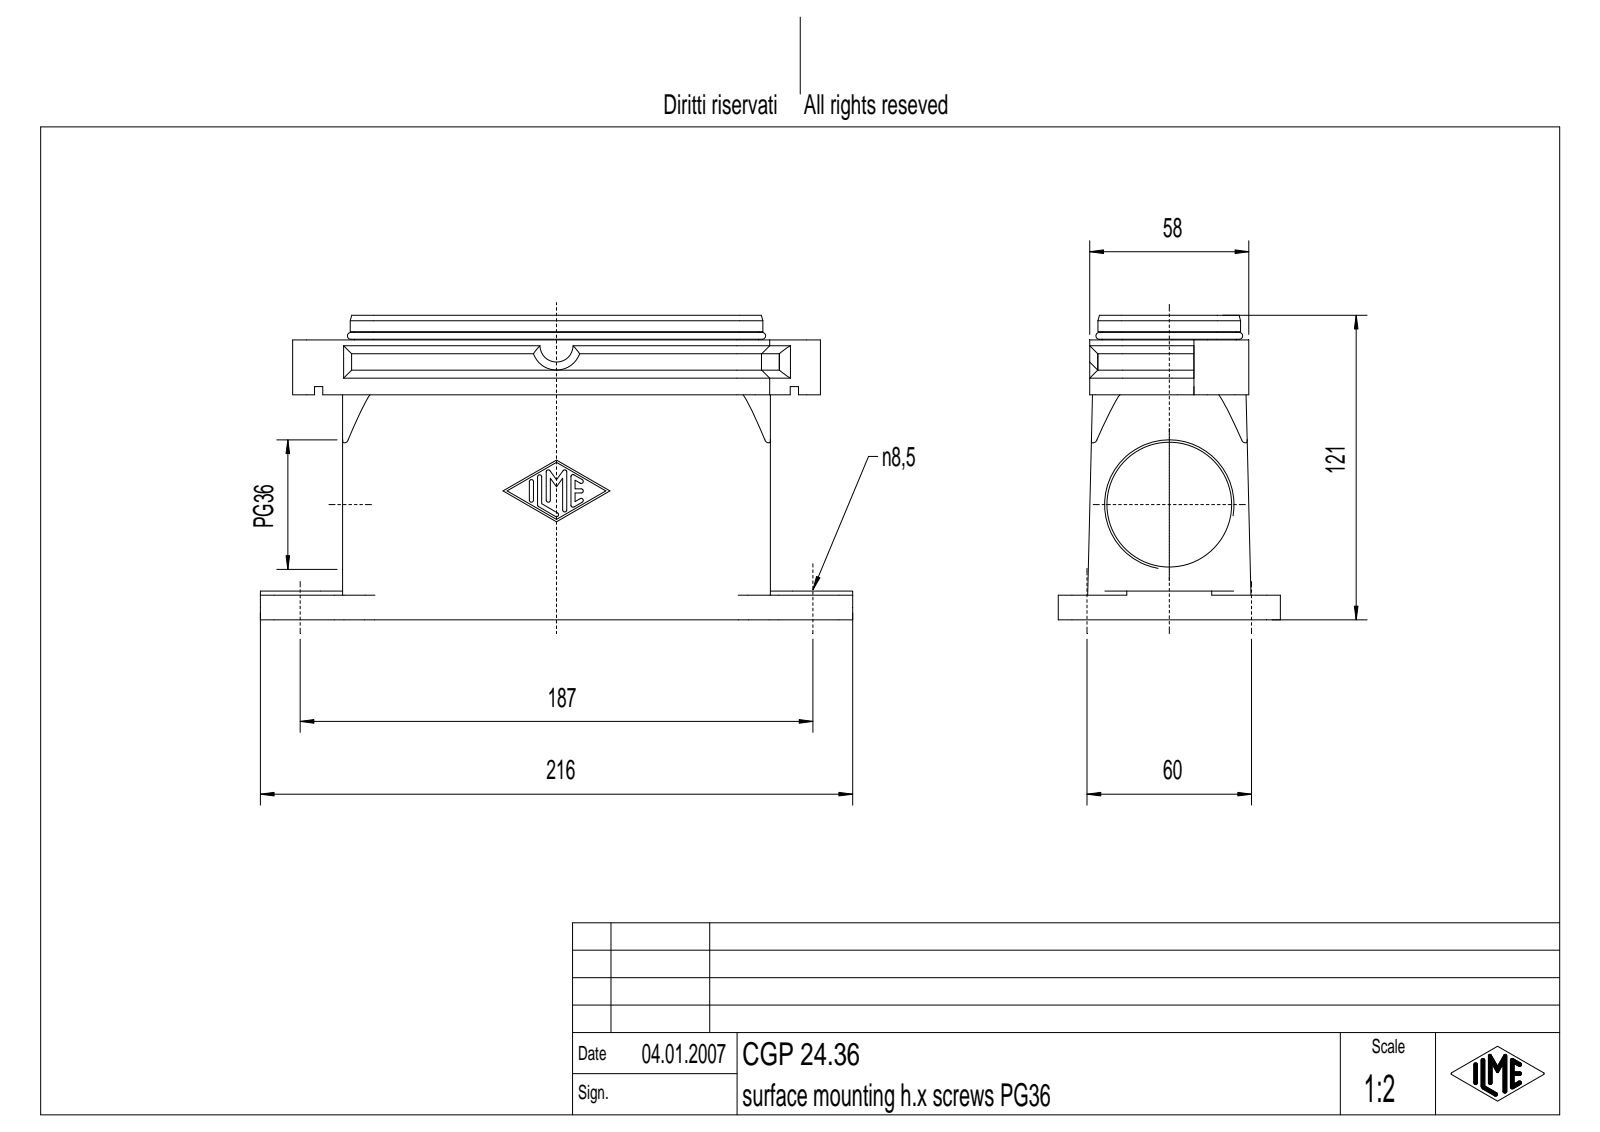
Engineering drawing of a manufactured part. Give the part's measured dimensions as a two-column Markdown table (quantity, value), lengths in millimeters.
| quantity | value |
| --- | --- |
| part name | MSBO9681 |
| STEP written by | CoCreate Modeling 16.00A 16-Aug-2008 (C) Parametric Technology GmbH (AUTOMOTIVE_DESIGN) |
| units | millimeters |
| bodies | 1 solid, 500 faces (264 planar, 172 cylindrical, 64 other) |
| overall size | 216 × 121 × 81 |
| volume | 420 898 mm³ |
| surface area | 136 804 mm² |
| round holes (diameter × count) | 8.5 × 5, 2.46 × 4, 4.13 × 4, 5.5 × 4, 3.24 × 2, 4.92 × 2, 14 × 2, 45.48 × 1 |
| round bosses / shafts (diameter × count) | 8.5 × 4, 5 × 4, 2.5 × 4 |
| partial cylindrical surfaces (radius × count) | 5 × 32, 0.75 × 14, 8 × 6, 1.5 × 4, 2 × 4, 3.25 × 4, 7 × 4, 8.5 × 4 |
| main face-to-face distances | 45.5, 10, 5.5, 9, 3, 112, 1, 150.5, 3.25, 6.25 |
| hole center spacings | 13.48, 16.03, 18.23, 31.53, 32.34, 41.9, 44.66, 53.98 |
